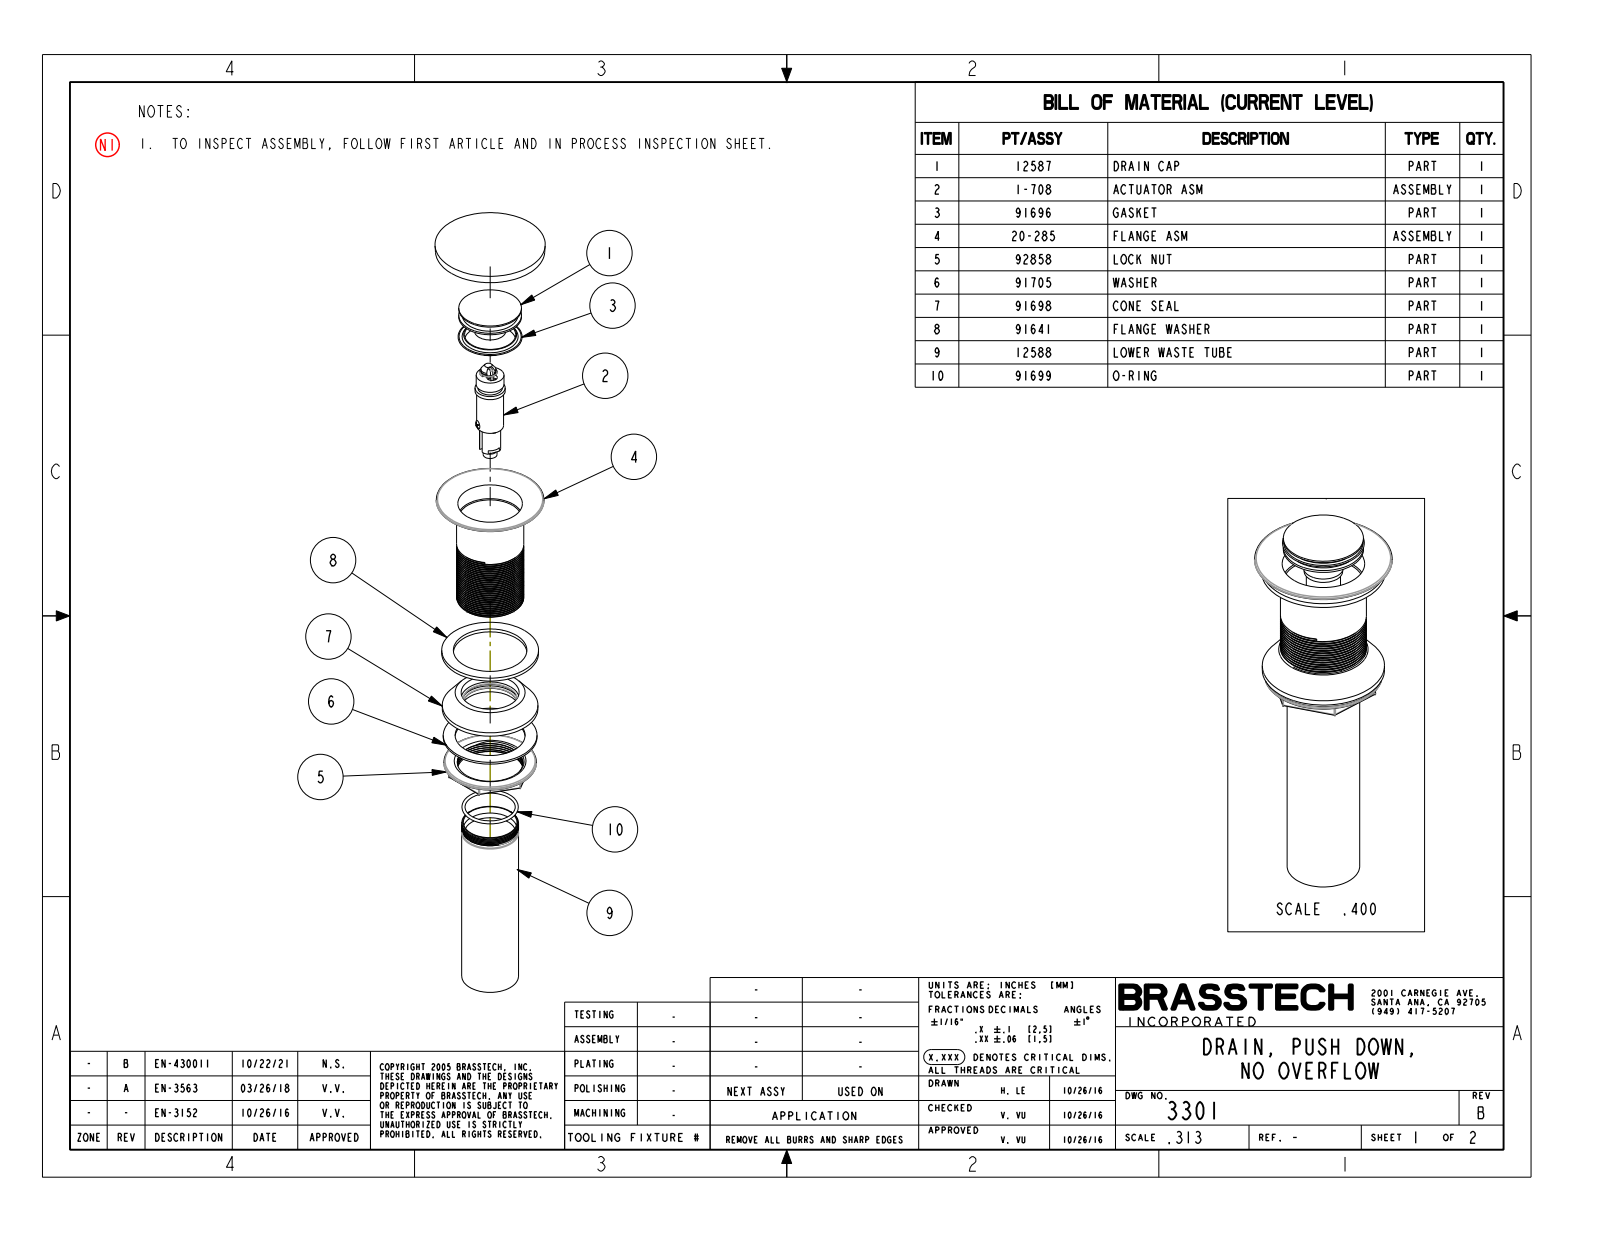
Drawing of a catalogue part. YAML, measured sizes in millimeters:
part_name: "3301"
step_written_by: "CREO PARAMETRIC BY PTC INC, 2018500 (CONFIG_CONTROL_DESIGN)"
units: millimeters
bodies: {solids: 3, faces: 289, planar: 46, cylindrical: 134, other: 109}
overall_size: [178.1, 60, 60]
volume: 125200
surface_area: 67290
round_holes:
  - {diameter: 29.9, count: 1}
  - {diameter: 30, count: 1}
  - {diameter: 31.2, count: 1}
  - {diameter: 32.5, count: 1}
  - {diameter: 34, count: 1}
  - {diameter: 35, count: 1}
  - {diameter: 36, count: 1}
  - {diameter: 36.6, count: 1}
  - {diameter: 39, count: 1}
  - {diameter: 41, count: 1}
round_bosses_or_shafts:
  - {diameter: 1.3, count: 3}
  - {diameter: 60, count: 1}
  - {diameter: 54, count: 1}
  - {diameter: 53.3, count: 1}
  - {diameter: 52.3, count: 1}
  - {diameter: 51.5, count: 1}
  - {diameter: 37.5, count: 1}
  - {diameter: 35, count: 1}
partial_cylinders:
  - {radius: 0.5, count: 18}
  - {radius: 1.5, count: 4}
face_to_face_distances: [2, 36.1, 34.1, 1.2, 5.2, 39.3, 41.3, 4, 38.1, 40.1]
